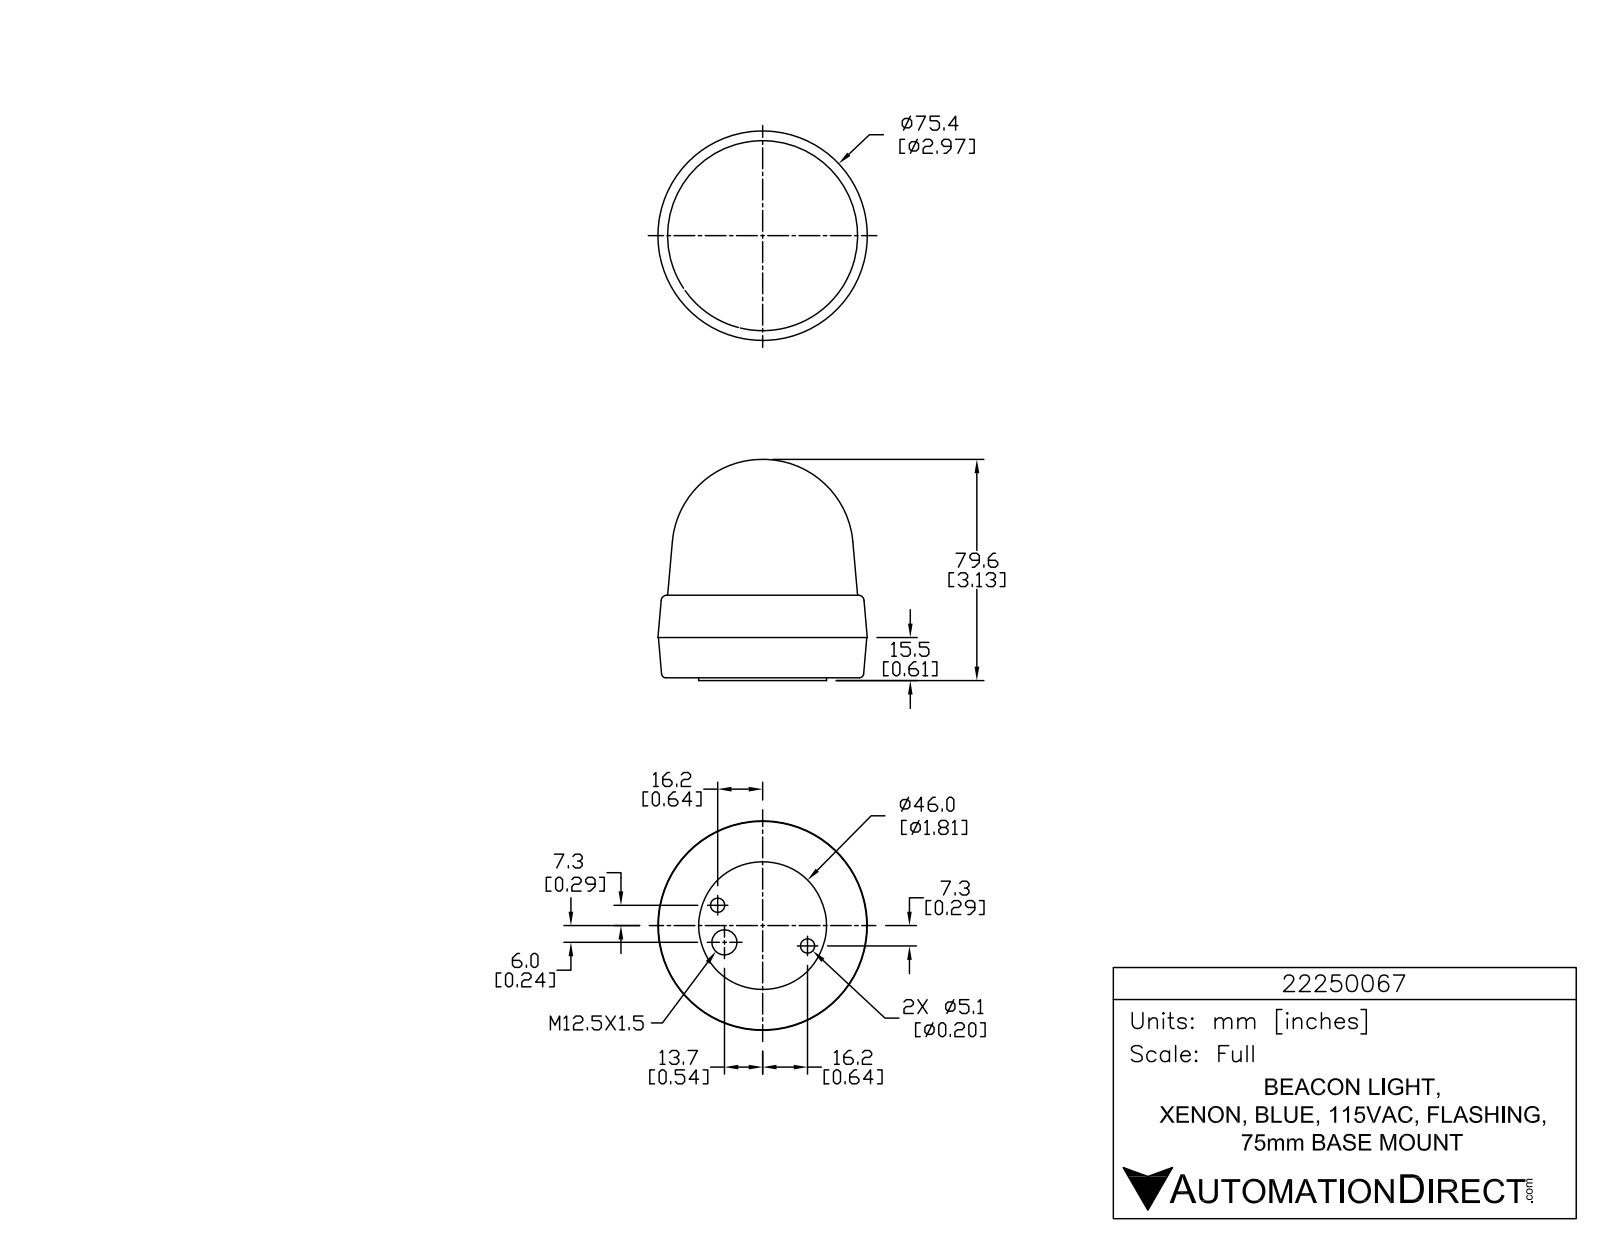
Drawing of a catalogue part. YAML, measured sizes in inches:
part_name: "22250067"
step_written_by: "SolidWorks 2015 (AUTOMOTIVE_DESIGN)"
units: inches
bodies: {solids: 1, faces: 773, planar: 526, cylindrical: 163, other: 84}
overall_size: [3.133, 2.967, 2.967]
volume: 15.79
surface_area: 33.7
round_holes:
  - {diameter: 0.059, count: 3}
  - {diameter: 0.201, count: 2}
  - {diameter: 0.354, count: 1}
round_bosses_or_shafts:
  - {diameter: 0.339, count: 3}
  - {diameter: 0.084, count: 3}
  - {diameter: 1.811, count: 1}
partial_cylinders:
  - {radius: 0.005, count: 9}
  - {radius: 0.005, count: 6}
  - {radius: 0.012, count: 6}
  - {radius: 0.012, count: 6}
  - {radius: 0.012, count: 6}
  - {radius: 0.196, count: 6}
  - {radius: 0.005, count: 3}
  - {radius: 0.005, count: 3}
face_to_face_distances: [0.039, 1.209, 1.17, 0.61, 0.571, 0.599, 1.566, 1.527, 0.956, 0.357]
hole_center_spacings: [0.534, 1.179, 1.398]
